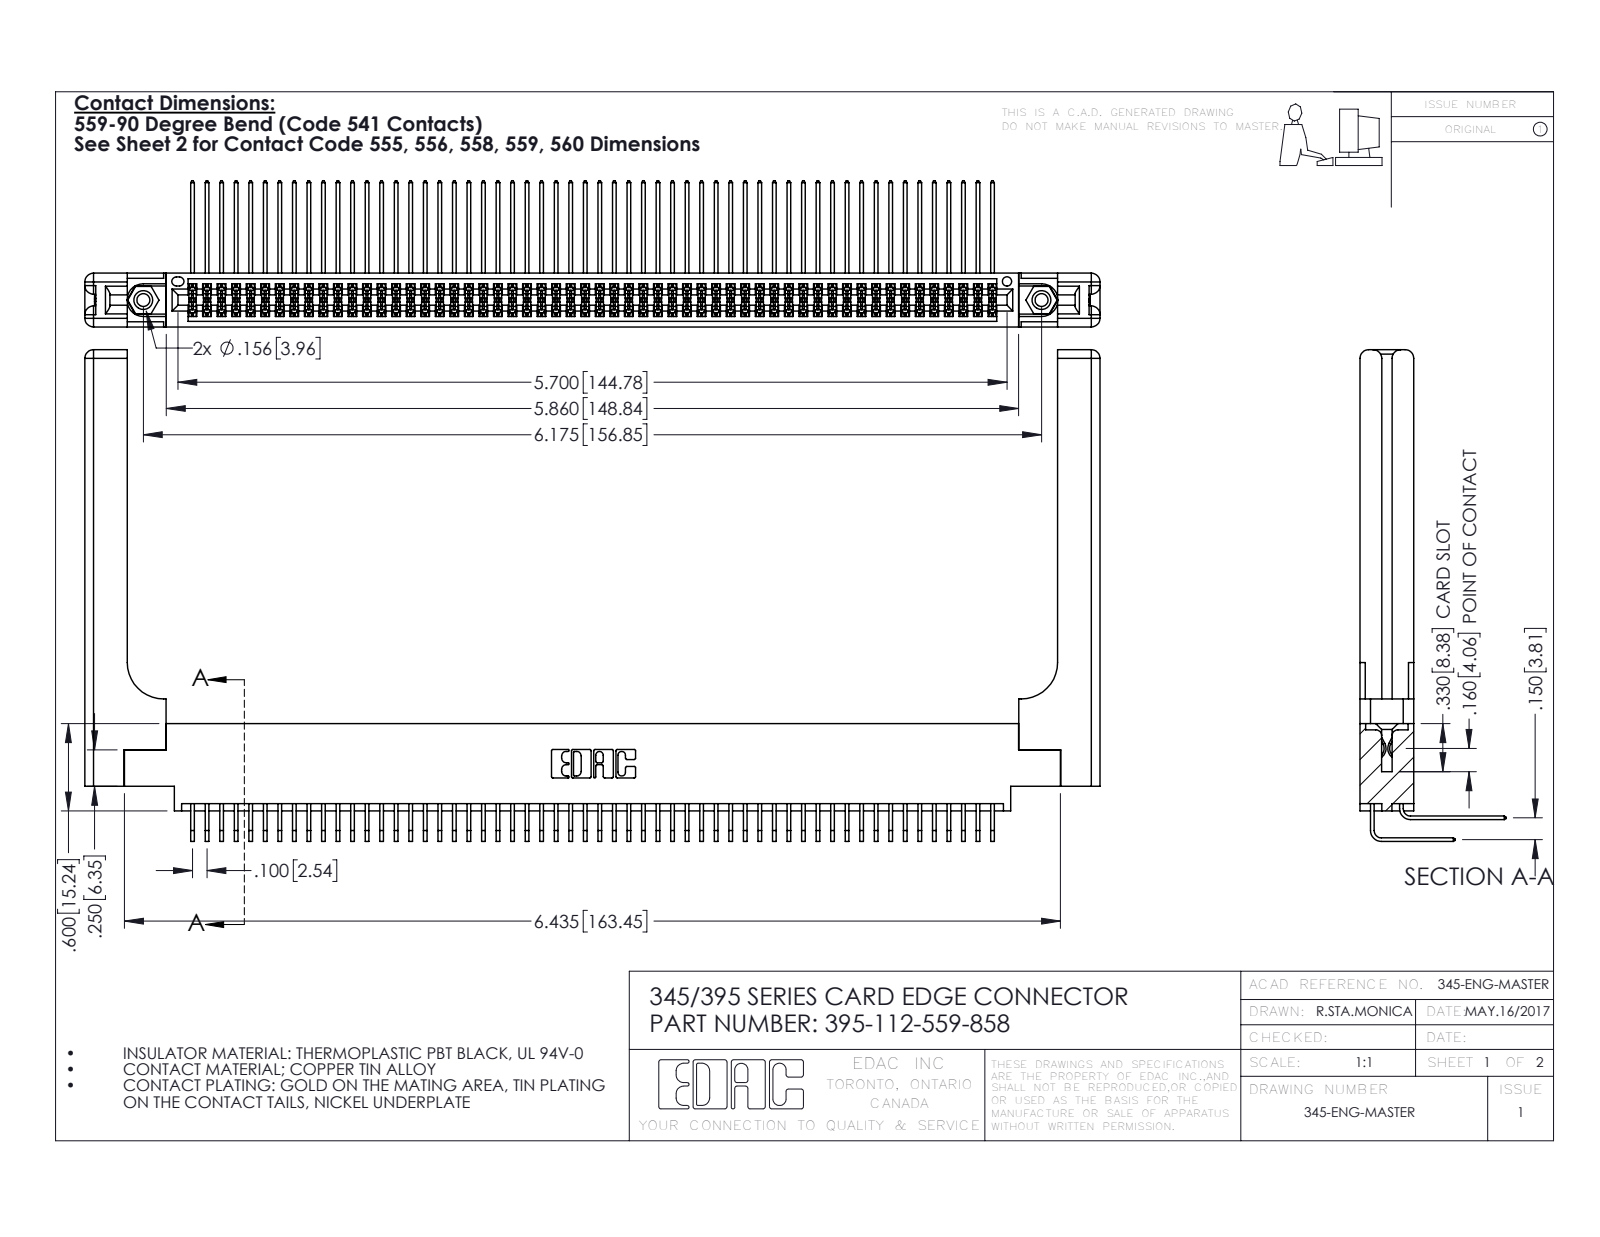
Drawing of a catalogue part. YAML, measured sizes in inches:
part_name: "345-292-001_558 559 Tail - 1; 345-250-001_345-250-001-102; 345-220-058_345-220-058; 345 Part_0.170 Offset - 0.156 Dia-TH (+2 more)"
step_written_by: "SolidWorks 2016 (CONFIG_CONTROL_DESIGN)"
units: inches
bodies: {solids: 117, faces: 6210, planar: 4152, cylindrical: 1998, other: 60}
overall_size: [6.979, 3.379, 1.005]
volume: 1.608
surface_area: 54.16
round_holes:
  - {diameter: 0.089, count: 2}
  - {diameter: 0.125, count: 2}
  - {diameter: 0.156, count: 2}
  - {diameter: 0.064, count: 1}
round_bosses_or_shafts:
  - {diameter: 0.155, count: 2}
partial_cylinders:
  - {radius: 0.006, count: 168}
  - {radius: 0.01, count: 22}
  - {radius: 0.06, count: 16}
  - {radius: 0.007, count: 6}
  - {radius: 0.031, count: 6}
  - {radius: 0.026, count: 3}
  - {radius: 0.014, count: 2}
  - {radius: 0.019, count: 2}
face_to_face_distances: [0.072, 0.298, 0.37, 0.098, 0.272, 0.025, 0.2, 0.225, 0.175, 0.15]
hole_center_spacings: [0.27, 5.939, 6.175]
